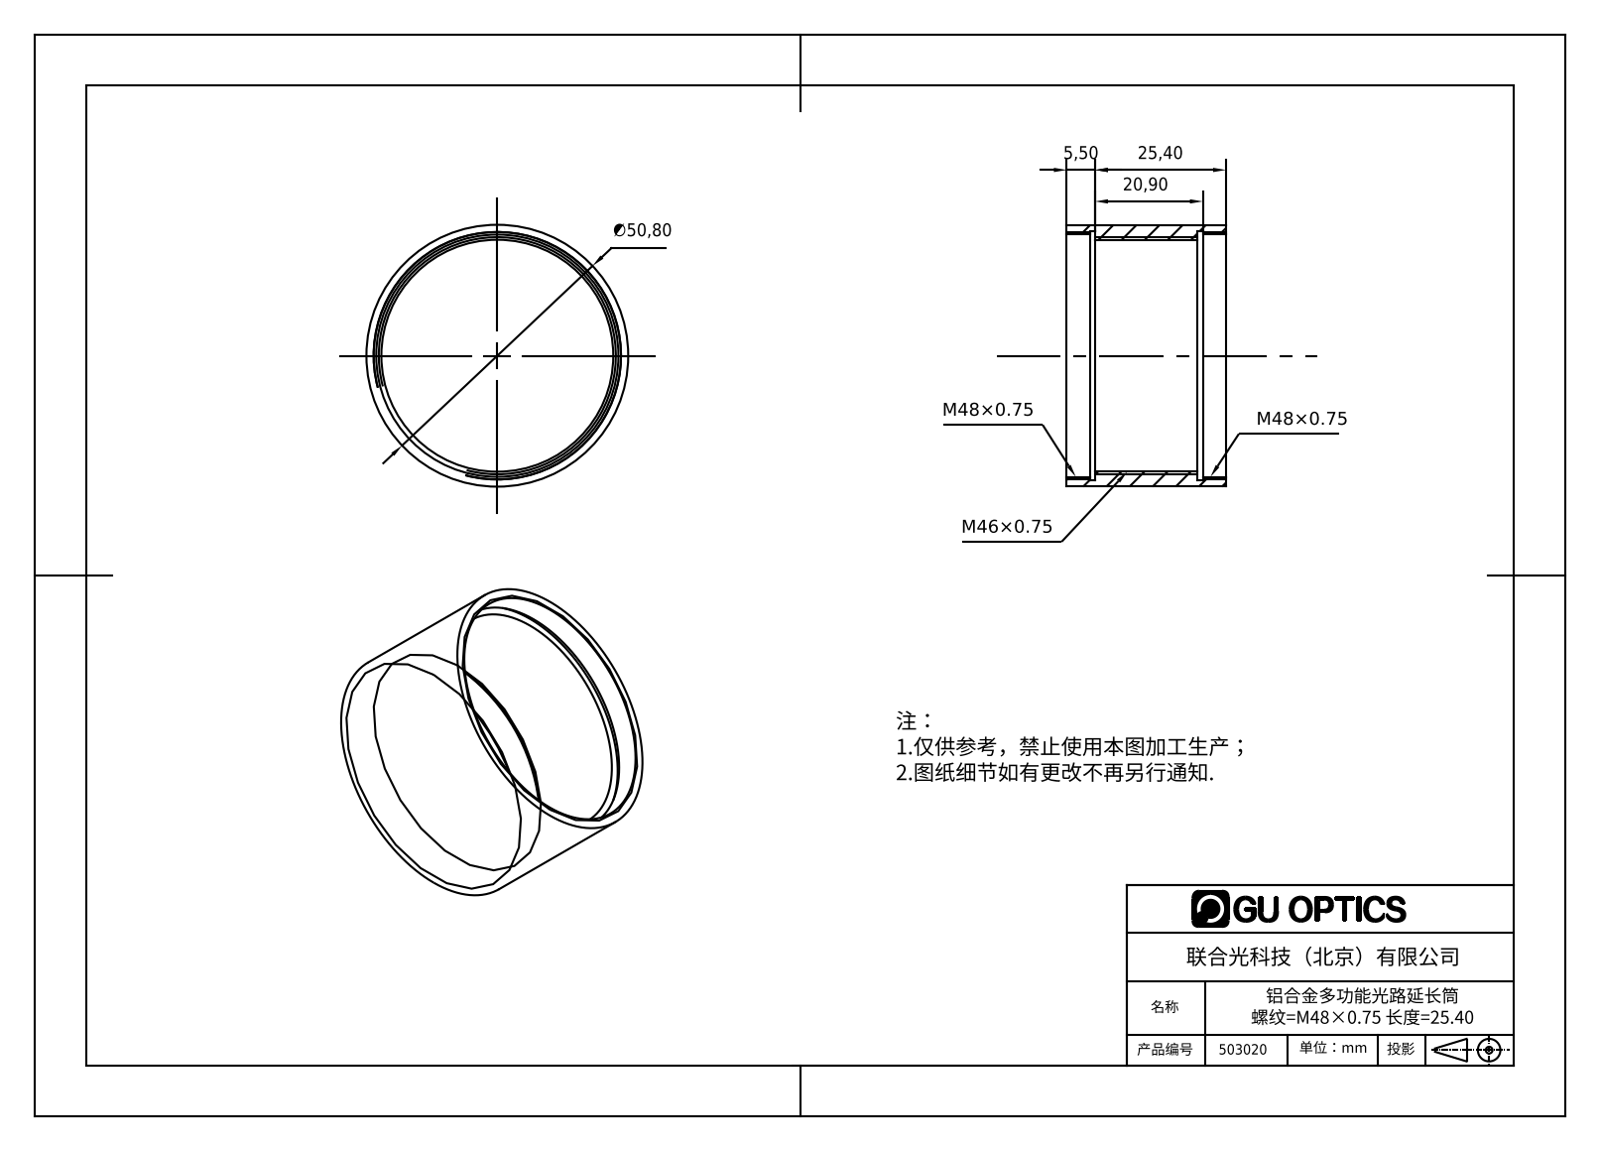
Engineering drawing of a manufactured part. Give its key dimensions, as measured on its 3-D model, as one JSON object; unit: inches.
{"part_name": "503020", "step_written_by": "SolidWorks 2016 (AUTOMOTIVE_DESIGN)", "units": "inches", "bodies": {"solids": 1, "faces": 18, "planar": 6, "cylindrical": 12, "other": 0}, "overall_size": [2, 2, 1.217], "volume_in3": 0.715, "surface_area_in2": 16.44, "round_holes": [[1.772, 1], [1.85, 1], [1.898, 1]], "round_bosses_or_shafts": [[2, 1]], "face_to_face_distances": [0.217, 1, 1.217, 0.783, 0.177, 1.039, 0.039, 0.823, 0.862]}
